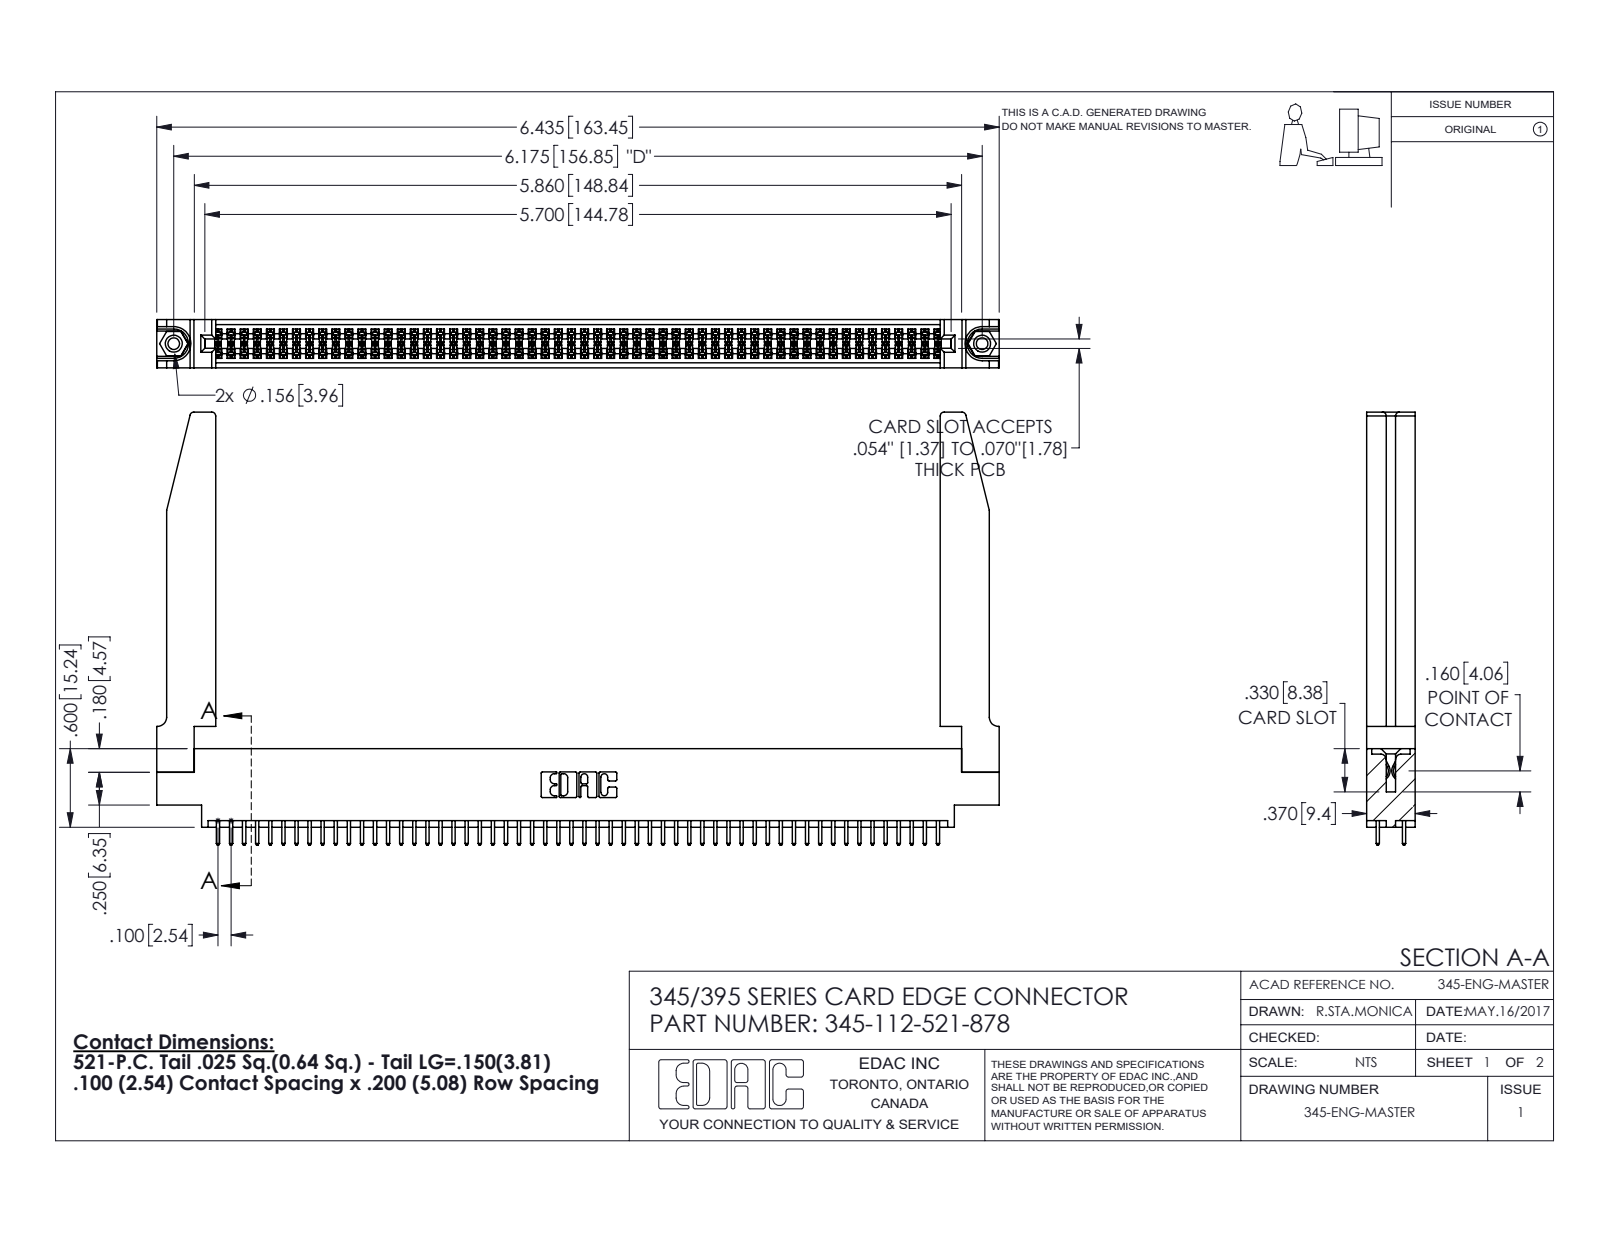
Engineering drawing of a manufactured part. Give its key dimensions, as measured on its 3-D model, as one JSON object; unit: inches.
{"part_name": "345-112-521-878; 345-250-001_345-250-001-102; 345-292-001_345-293-121; 345 Part_0.170 Offset - 0.156 Dia-TH (+1 more)", "step_written_by": "SolidWorks 2016 (CONFIG_CONTROL_DESIGN)", "units": "inches", "bodies": {"solids": 117, "faces": 5964, "planar": 3922, "cylindrical": 1990, "other": 52}, "overall_size": [6.436, 3.307, 0.37], "volume_in3": 1.441, "surface_area_in2": 47.1, "round_holes": [[0.089, 2], [0.125, 2], [0.156, 2], [0.064, 1]], "round_bosses_or_shafts": [[0.155, 2]], "partial_cylinders_radius": [[0.006, 168], [0.01, 112], [0.01, 22], [0.03, 8], [0.007, 6], [0.031, 6], [0.026, 3], [0.014, 2]], "face_to_face_distances": [0.072, 0.298, 0.37, 0.098, 0.272, 0.025, 0.2, 0.225, 0.175, 0.148], "hole_center_spacings": [0.27, 5.939, 6.175]}
